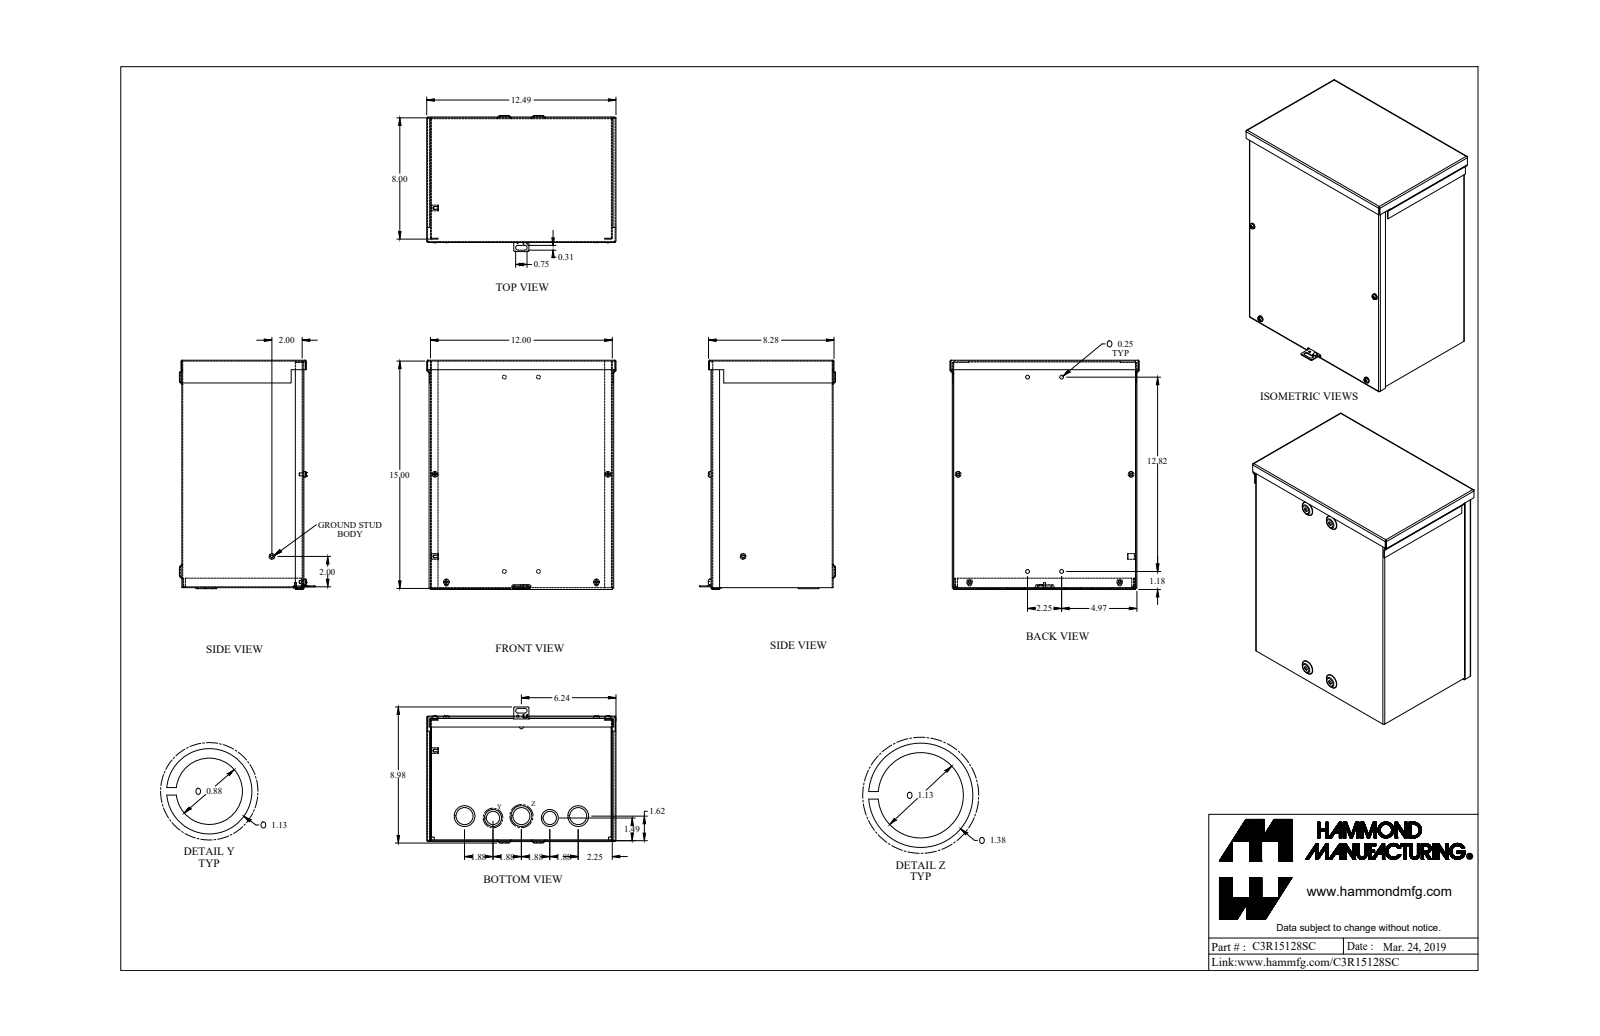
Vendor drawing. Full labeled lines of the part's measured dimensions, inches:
Part name (STEP PRODUCT): C3R15128SC_Default
STEP written by: SolidWorks 2019 (CONFIG_CONTROL_DESIGN)
Units: inches
Bodies: 11 solids, 429 faces (226 planar, 117 cylindrical, 86 other)
Overall size (bounding box): 15.12 × 12.489 × 8.977
Volume: 51.01 in³ · Surface area: 1 800 in²
Round holes (diameter × count): ⌀0.17 ×4, ⌀0.25 ×4, ⌀1.125 ×3, ⌀0.875 ×2, ⌀0.125 ×1, ⌀0.137 ×1, ⌀0.156 ×1
Round bosses / shafts (diameter × count): ⌀0.19 ×4, ⌀1.375 ×3, ⌀0.375 ×3, ⌀1.125 ×2, ⌀0.375 ×2, ⌀0.125 ×1
Partial cylindrical surfaces — rounded edges, fillets, slot ends (radius × count): R0.029 ×21, R0.086 ×21, R0.109 ×8, R0.125 ×8, R0.156 ×2
Main face-to-face distances: 0.057, 8, 11.943, 7.943, 8.057, 12, 0.057, 11.886, 14.886, 14.943
Hole centre spacings: 7.879, 9.368, 3.75, 1.879, 1.88, 2.25, 3.92, 6.142
